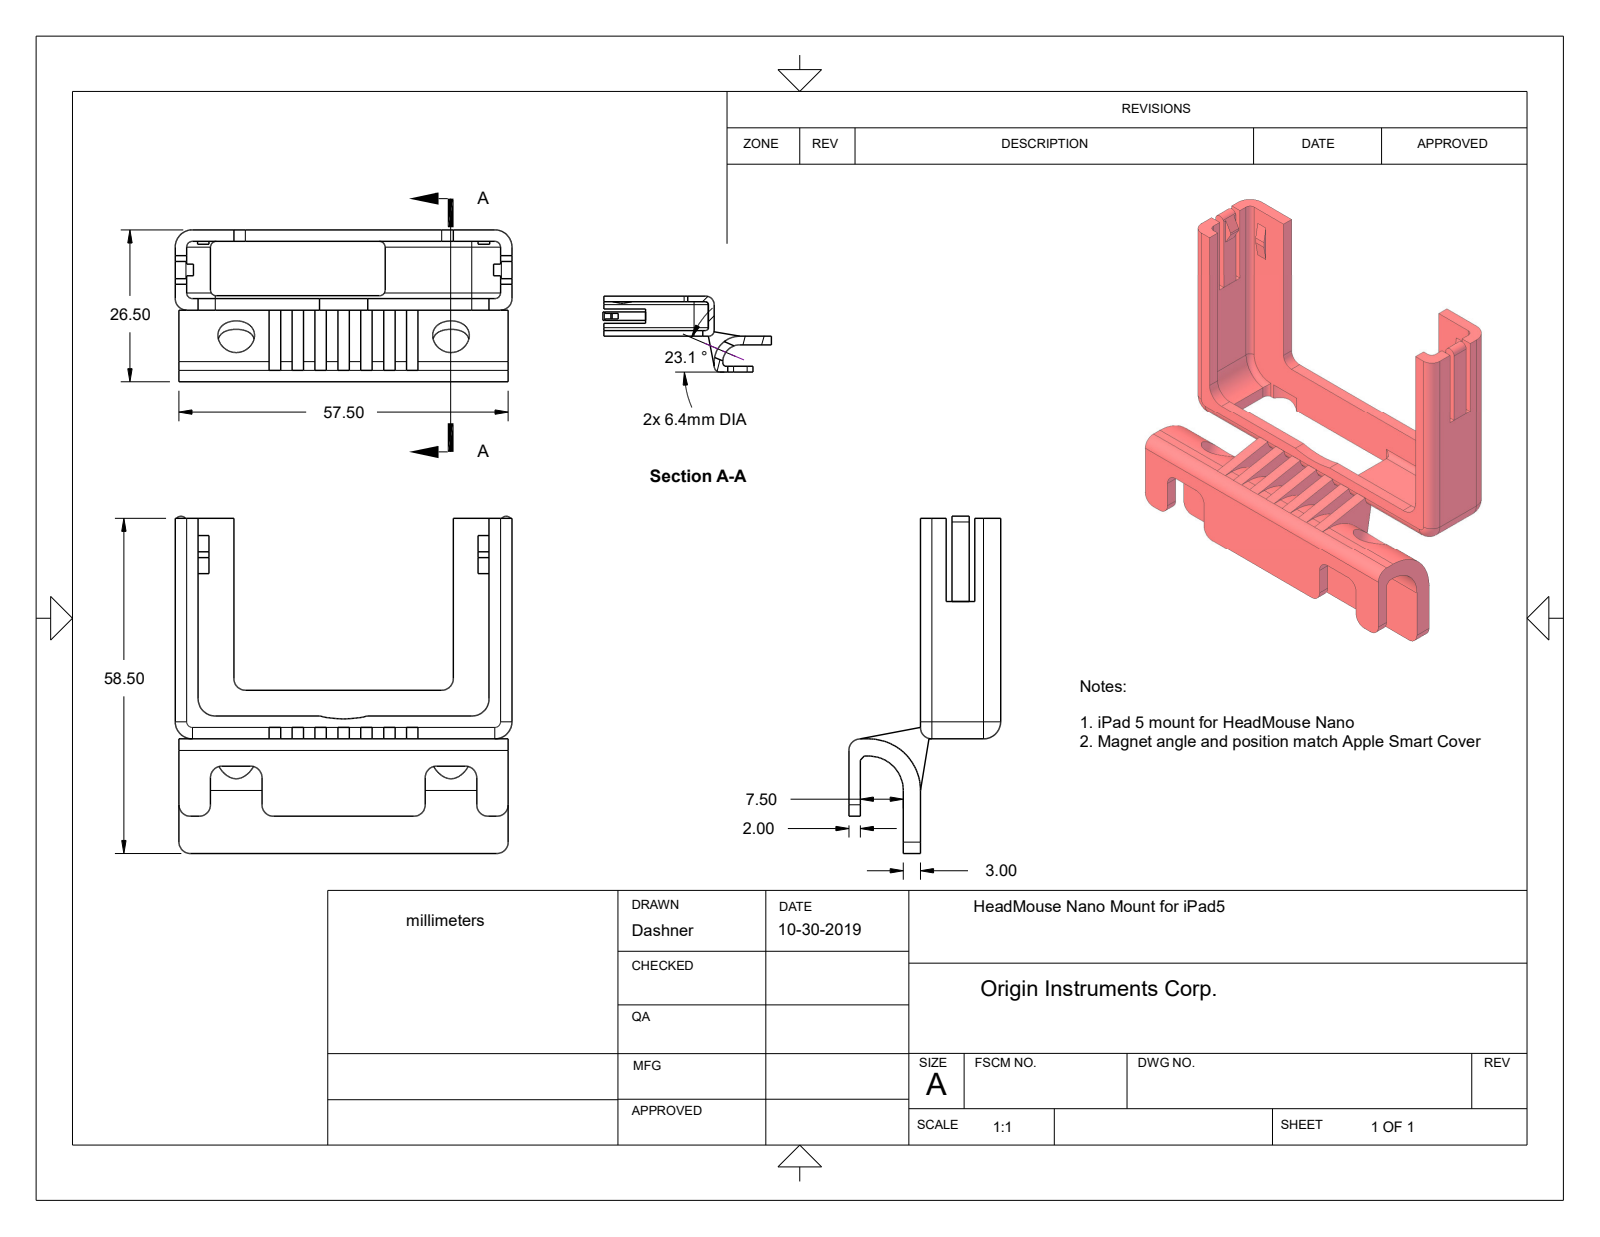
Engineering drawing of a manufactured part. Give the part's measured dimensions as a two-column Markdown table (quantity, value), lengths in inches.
| quantity | value |
| --- | --- |
| part name | HMN_SnapTray; SNAP_8x3x1mm; iPad5_Interface-3; iPad-5-5_HMN_SnapTray |
| STEP written by | Alibre (CONFIG_CONTROL_DESIGN) |
| units | inches |
| bodies | 4 solids, 189 faces (122 planar, 59 cylindrical, 8 other) |
| overall size | 2.318 × 2.315 × 1.043 |
| volume | 0.648 in³ |
| surface area | 16.59 in² |
| round holes (diameter × count) | 0.252 × 2 |
| partial cylindrical surfaces (radius × count) | 0.079 × 18, 0.039 × 12, 0.118 × 7, 0.197 × 2, 0.177 × 1, 0.236 × 1, 0.354 × 1, 0.709 × 1 |
| main face-to-face distances | 0.079, 0.472, 0.965, 0.551, 0.118, 0.591, 0.669, 0.374, 0.492, 0.295 |
| hole center spacings | 1.476 |
